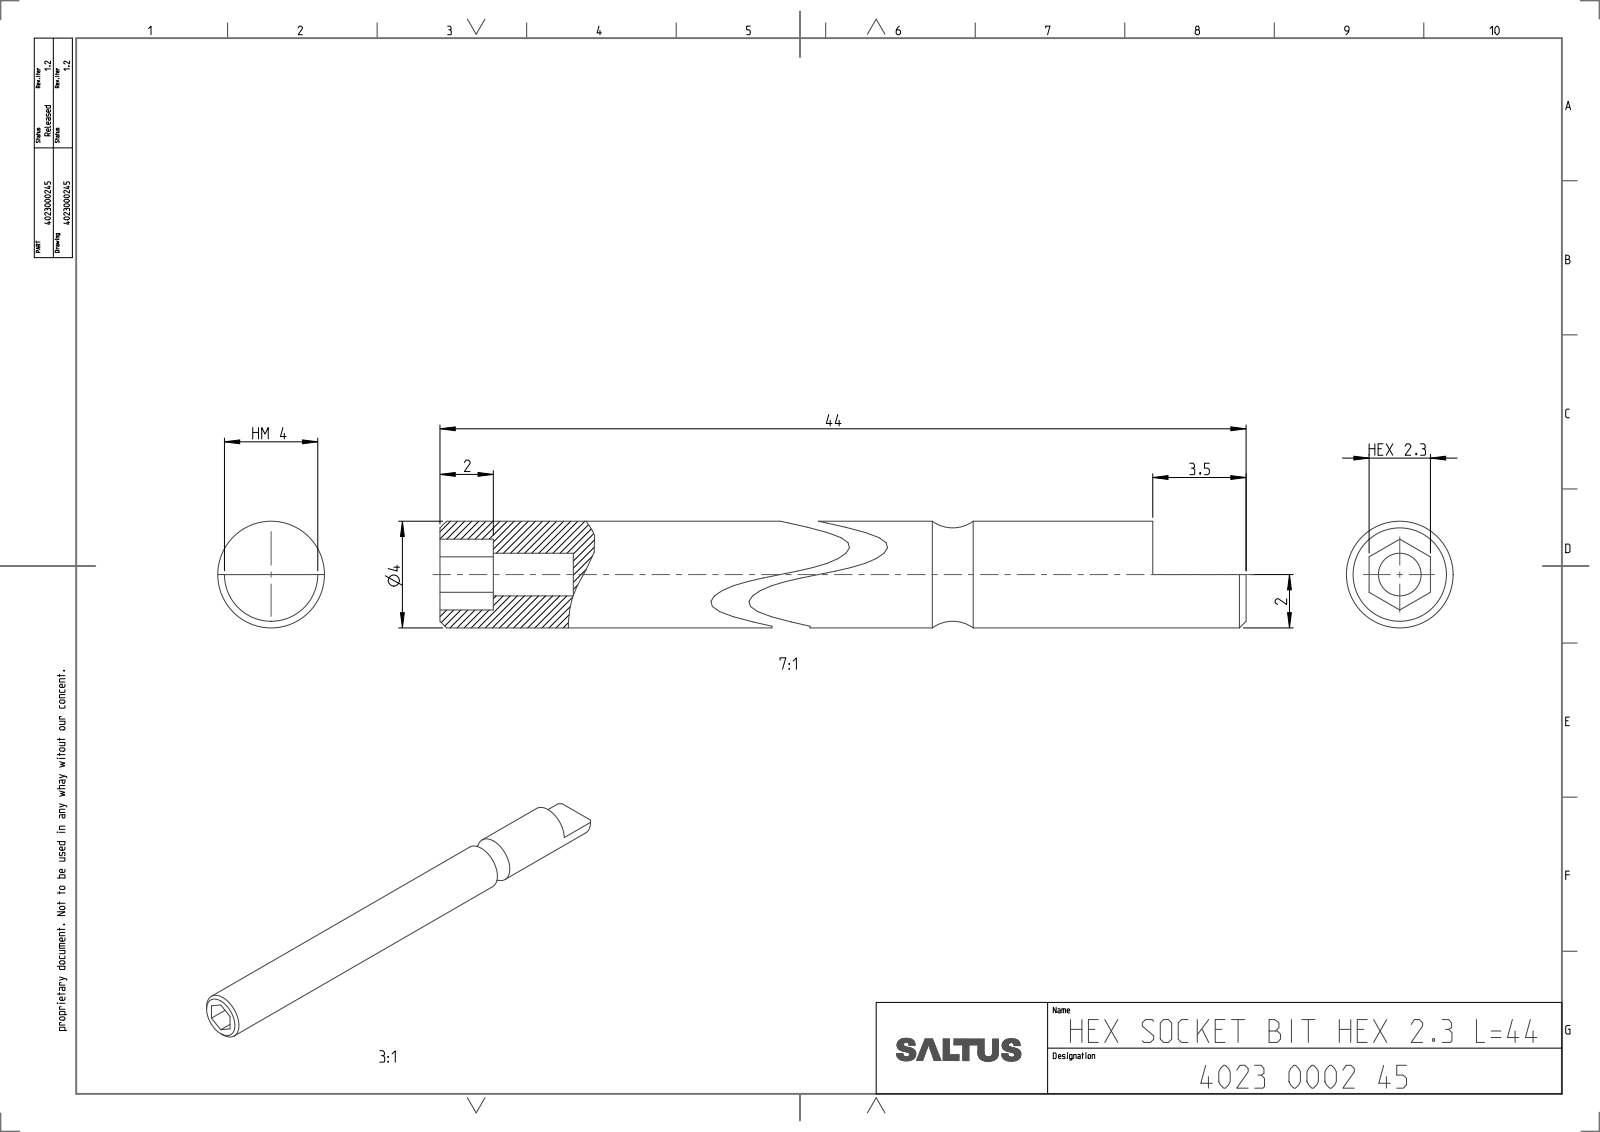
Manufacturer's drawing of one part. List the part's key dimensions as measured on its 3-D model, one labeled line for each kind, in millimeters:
Part name (STEP PRODUCT): 4023000245
STEP written by: CREO PARAMETRIC BY PTC INC, 2022414 (CONFIG_CONTROL_DESIGN)
Units: millimetres
Bodies: 1 solid, 23 faces (12 planar, 6 cylindrical, 5 other)
Overall size (bounding box): 44 × 4 × 4
Volume: 512 mm³ · Surface area: 598 mm²
Round holes (diameter × count): ⌀1.6 ×1
Round bosses / shafts (diameter × count): ⌀4 ×1
Main face-to-face distances: 2.3, 40.5, 3.5, 44, 42, 38.5, 2, 39, 35.5, 3
